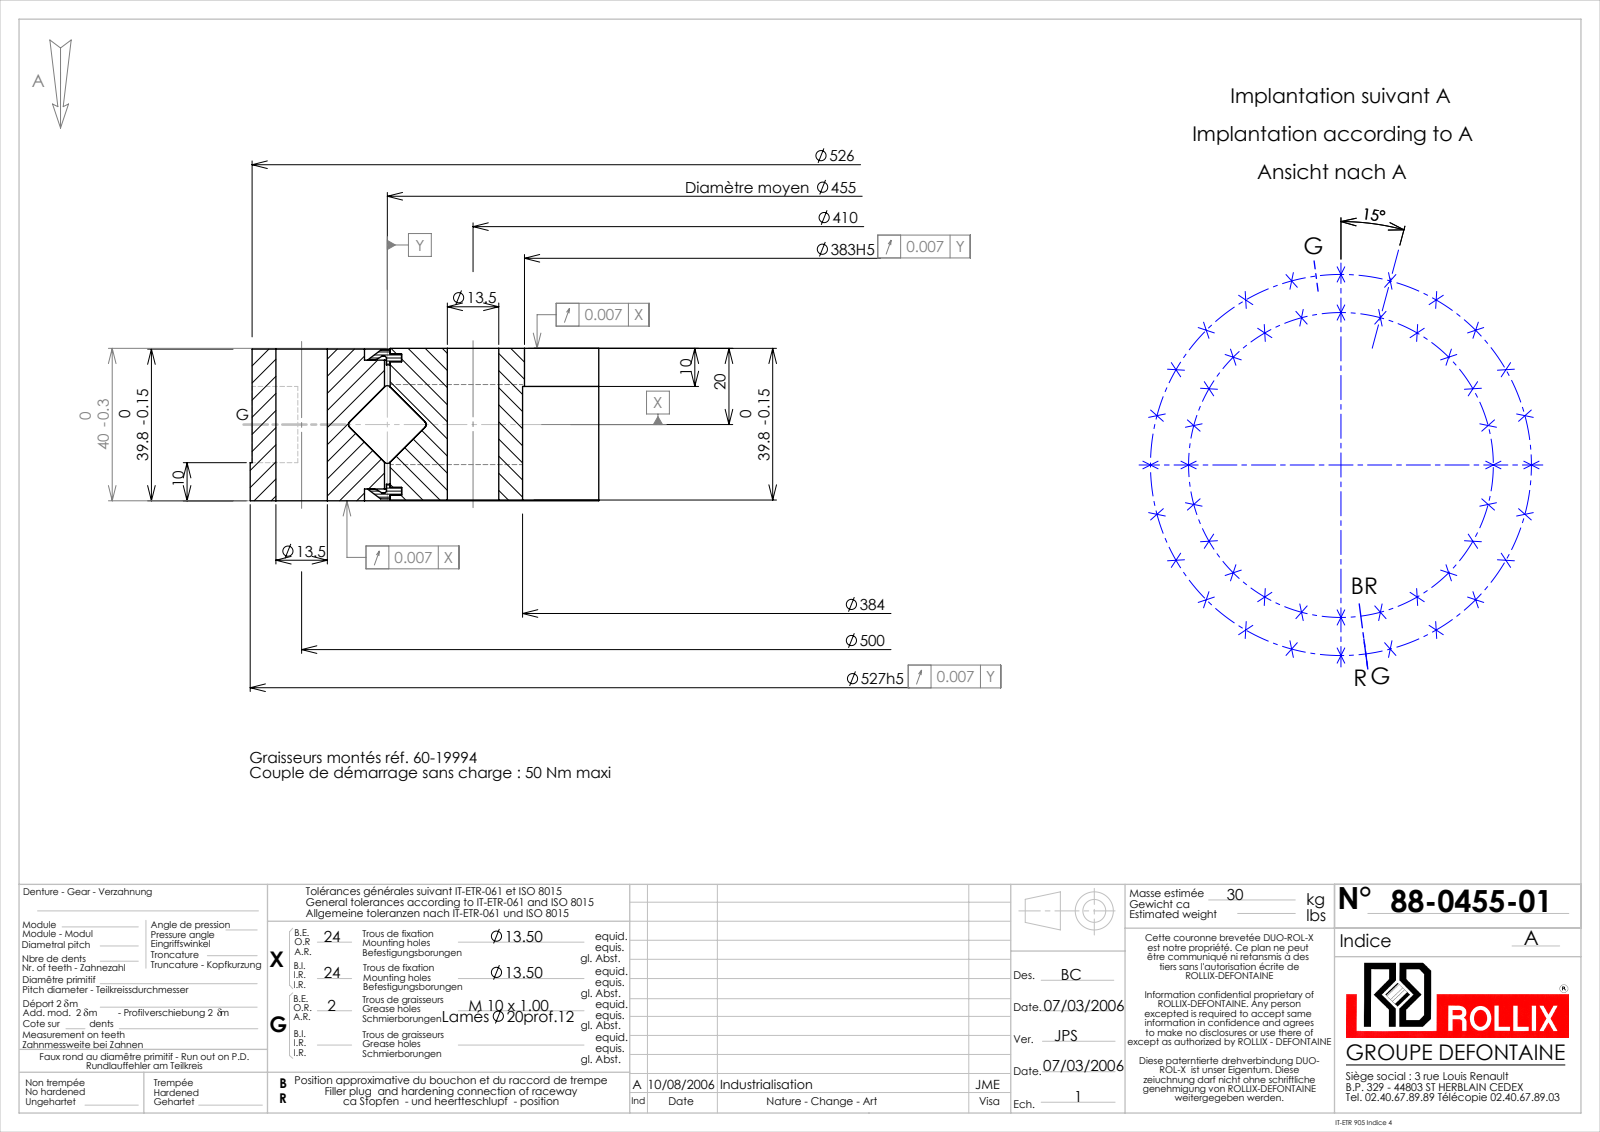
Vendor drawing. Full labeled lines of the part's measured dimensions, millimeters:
Part name (STEP PRODUCT): 88-0455-01
STEP written by: SolidWorks 2016 (CONFIG_CONTROL_DESIGN)
Units: millimetres
Bodies: 7 solids, 255 faces (46 planar, 154 cylindrical, 55 other)
Overall size (bounding box): 527 × 527 × 40
Volume: 3 395 000 mm³ · Surface area: 609 963 mm²
Round holes (diameter × count): ⌀13.5 ×48, ⌀9 ×2, ⌀20 ×2, ⌀383 ×1, ⌀384 ×1, ⌀447.5 ×1, ⌀453.5 ×1, ⌀456.5 ×1, ⌀467 ×1
Round bosses / shafts (diameter × count): ⌀10 ×2, ⌀527 ×1, ⌀526 ×1, ⌀455.5 ×1, ⌀15 ×1
Main face-to-face distances: 39.8, 39.6, 40, 3.1, 36.9, 2.9, 36.7, 1.5, 38.5, 1.3
Hole centre spacings: 250, 304.38, 461.94, 129.41, 65.27, 191.34, 396.68, 495.72
